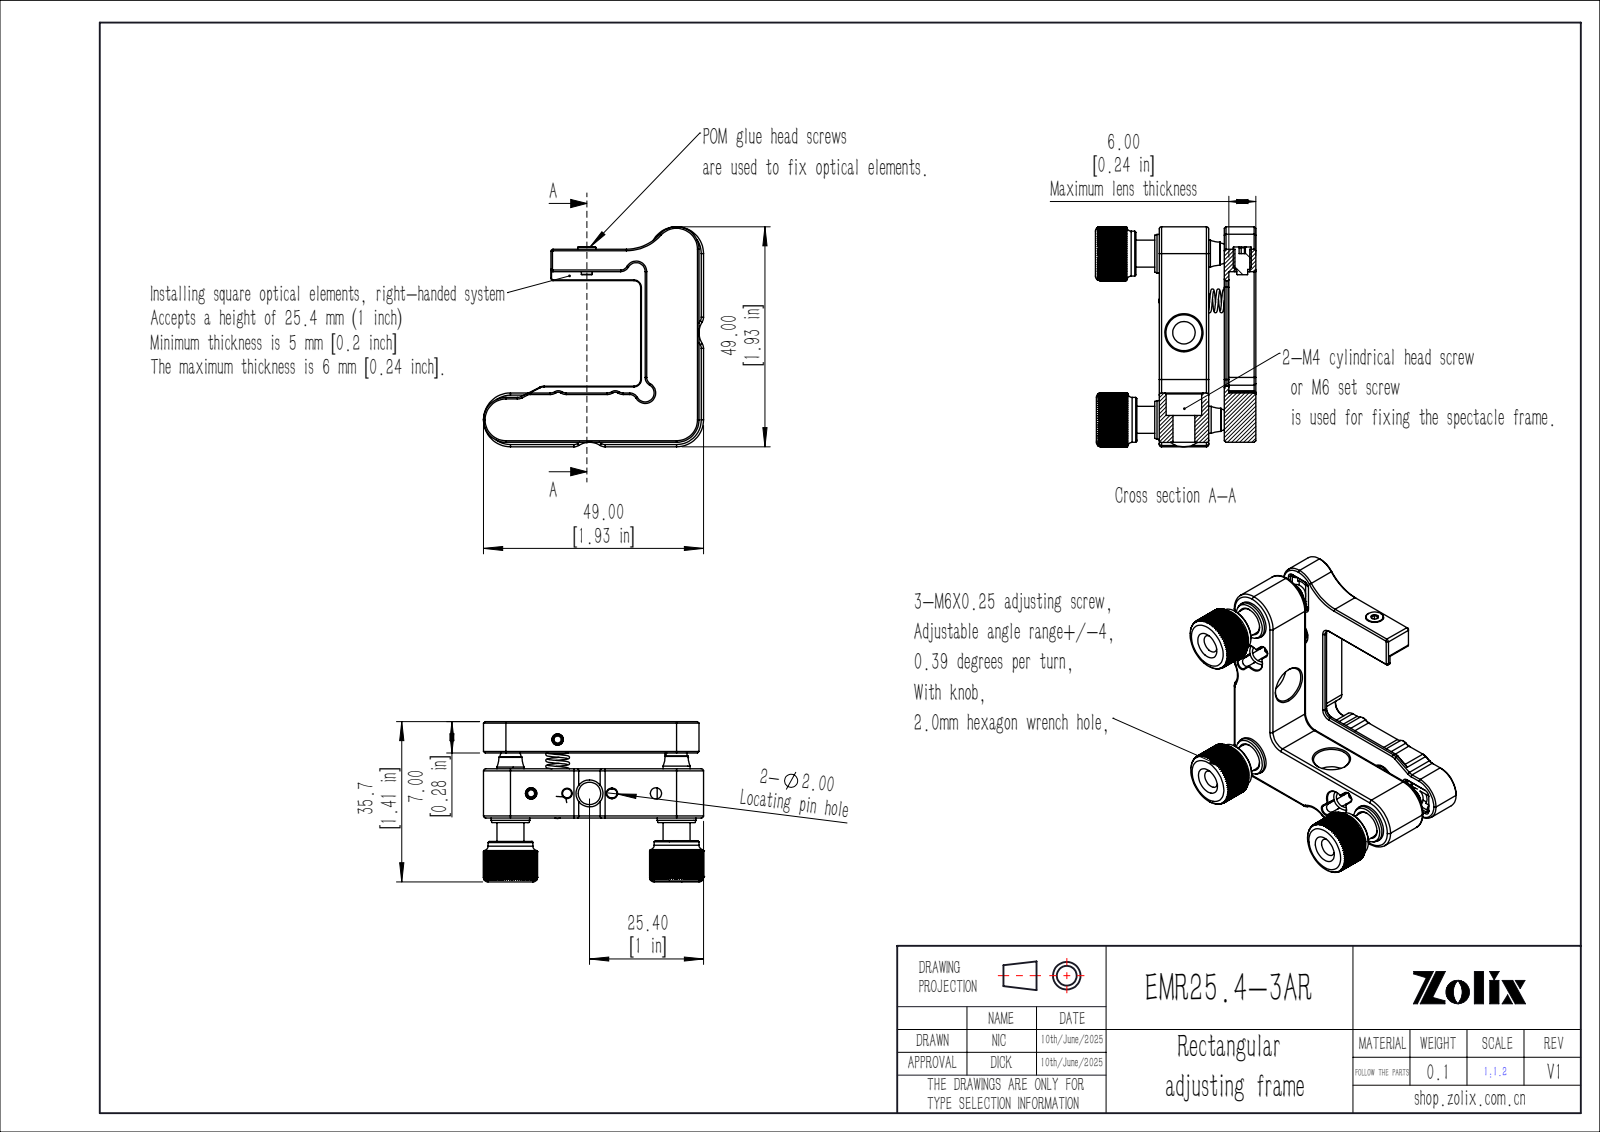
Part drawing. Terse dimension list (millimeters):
name: EMR25.4-3AR
written by: SolidWorks 2020 (CONFIG_CONTROL_DESIGN)
unit: mm
bodies: 0 solids, 1234 faces (623 planar, 379 cylindrical, 232 other)
size: 49 × 49 × 35.71
holes: 4× ⌀6, 3× ⌀4, 3× ⌀9.8, 2× ⌀2, 2× ⌀5, 2× ⌀8, 1× ⌀2.5, 1× ⌀3.3
bosses: 4× ⌀1.5, 3× ⌀10, 3× ⌀8.6, 3× ⌀6, 2× ⌀3, 2× ⌀2, 1× ⌀4, 1× ⌀2.4
rounds: 16× R2, 11× R0.5, 8× R0.8, 4× R1, 4× R1.1, 4× R1.5, 3× R4.75, 3× R6
face distances: 11, 7, 1, 10.5, 3.5, 12, 21.5, 14.5, 5, 8.2
hole spacings: 5, 10.5, 26.5, 37, 45.51, 13.01, 13.72, 14.8
